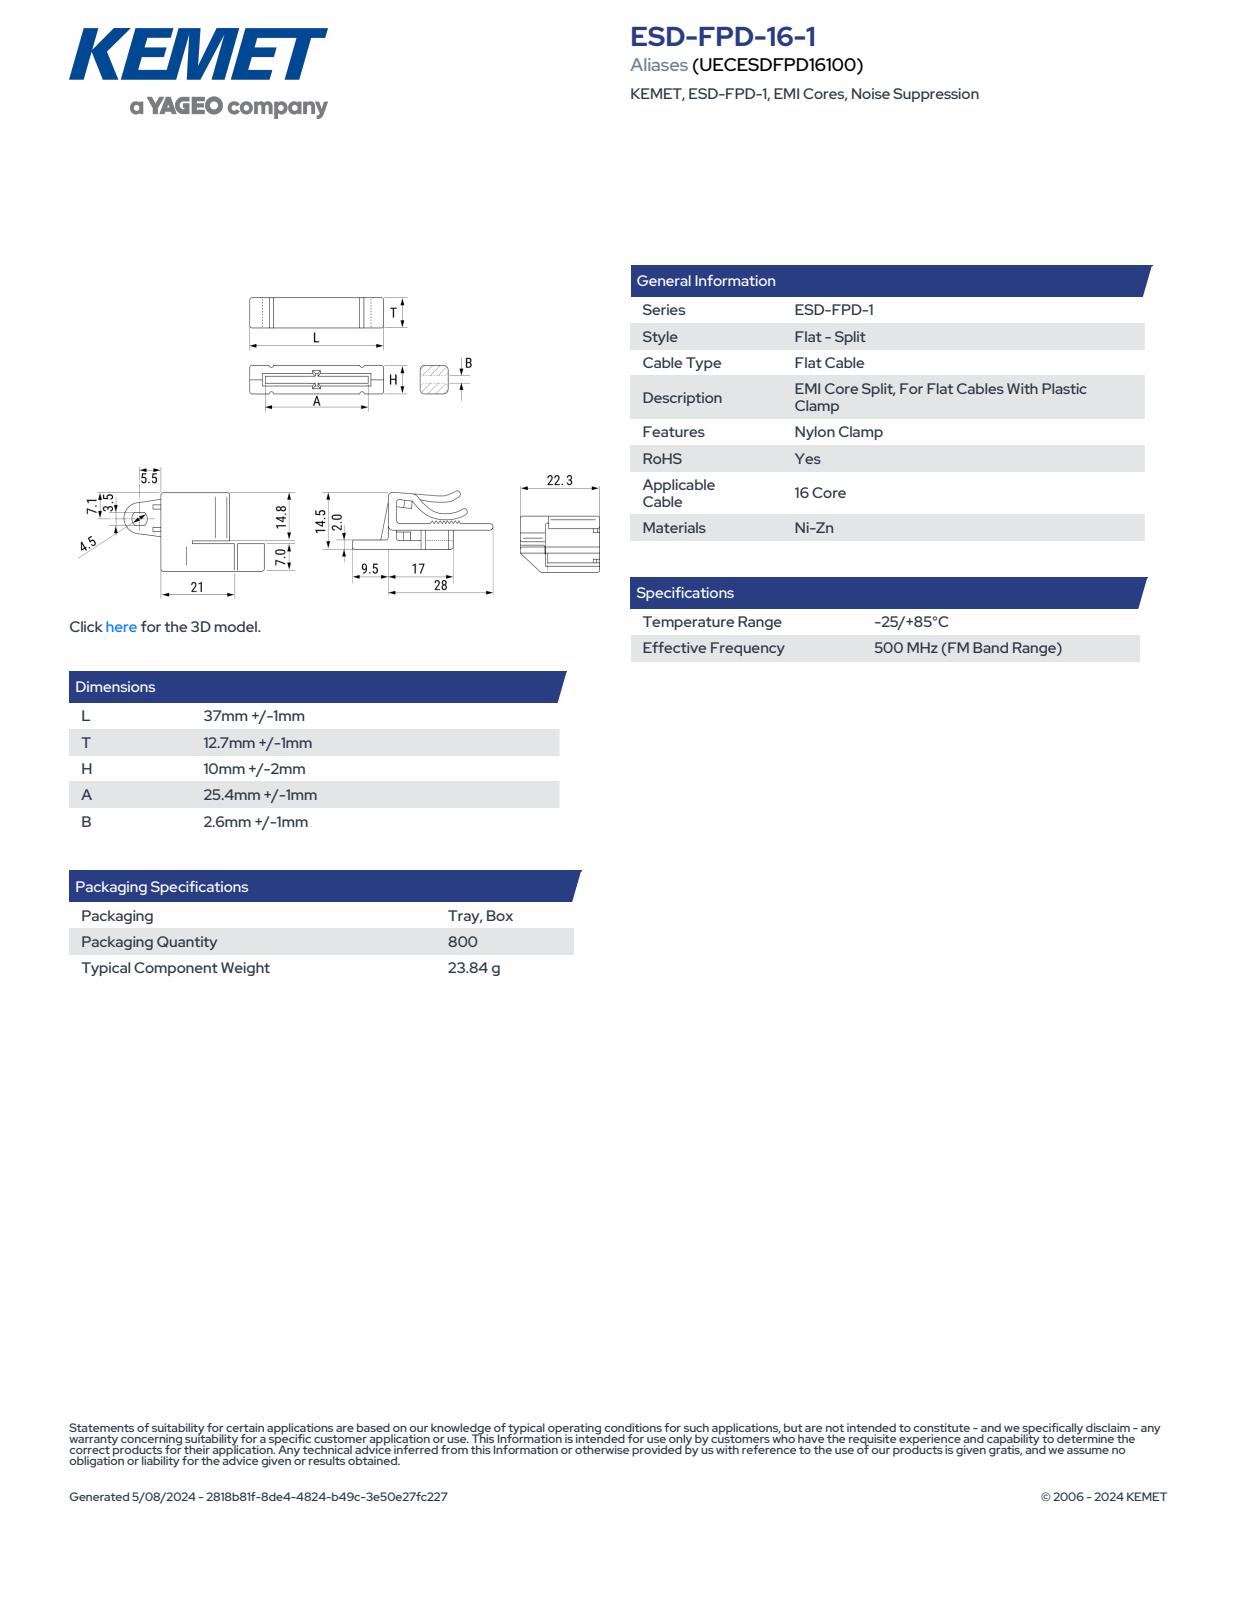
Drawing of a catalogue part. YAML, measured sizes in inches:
part_name: "EC_FPD1_L38T13.7H12A25.4B2.6"
step_written_by: "SolidWorks 2021 (AUTOMOTIVE_DESIGN)"
units: inches
bodies: {solids: 4, faces: 91, planar: 79, cylindrical: 12, other: 0}
overall_size: [1.496, 0.5, 0.472]
volume: 0.3
surface_area: 4.249
partial_cylinders:
  - {radius: 0.02, count: 8}
  - {radius: 0.024, count: 4}
face_to_face_distances: [0.185, 0.287, 0.472, 0.5, 0.102, 1.496, 0.248, 1.248, 0.66, 1]
